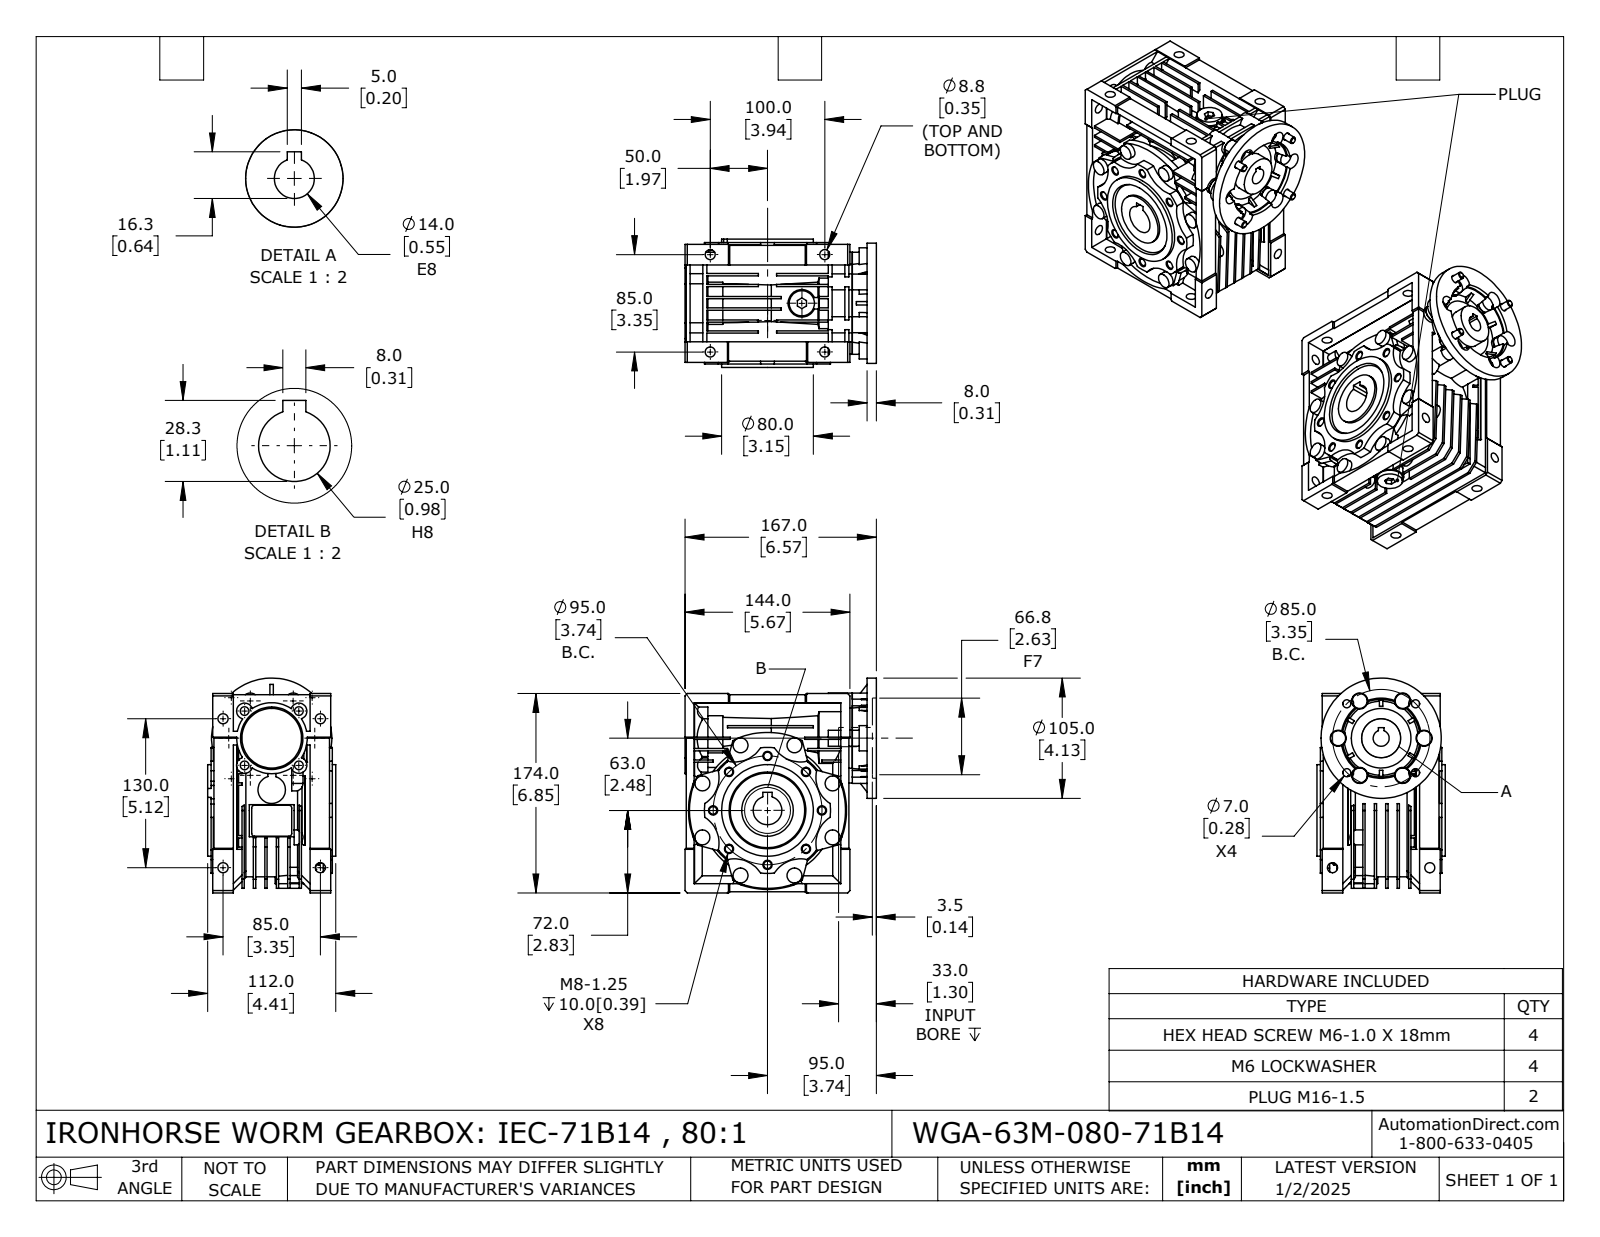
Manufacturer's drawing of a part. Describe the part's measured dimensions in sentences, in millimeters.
The part is named "WGA-63M-080-71B14". Its 3-D file was written by "SolidWorks 2024 (CONFIG_CONTROL_DESIGN)". It is 16 solids with 1428 faces: 836 planar, 417 cylindrical and 175 other. Overall it measures 187.5 by 175.5 by 112 millimeters. Its volume is 1 817 000 cubic millimeters and its surface area 341 752 square millimeters. Round holes: 8 of diameter 6.65, 8 of diameter 8.78, 4 of diameter 6.1, 4 of diameter 7, 4 of diameter 7.56, 2 of diameter 14.5, 1 of diameter 14, 1 of diameter 15, 1 of diameter 25, 1 of diameter 34, 1 of diameter 37, 1 of diameter 45. Round bosses or shafts: 14 of diameter 13, 4 of diameter 14, 4 of diameter 12.2, 4 of diameter 6, 3 of diameter 24, 2 of diameter 22, 2 of diameter 15.8, 2 of diameter 13.7. Partial cylindrical surfaces (rounded edges, fillets, slot ends): 12 of radius 7, 8 of radius 27, 6 of radius 6.98, 6 of radius 11, 4 of radius 2.5, 4 of radius 6, 1 of radius 8.35, 1 of radius 29.5. The main face-to-face distances are 10, 8, 20, 2, 30, 7, 12, 40, 18, 1. The hole center spacings are 36.36, 47.5, 54.12, 67.18, 87.77, 8.99, 33.5, 42.5.
